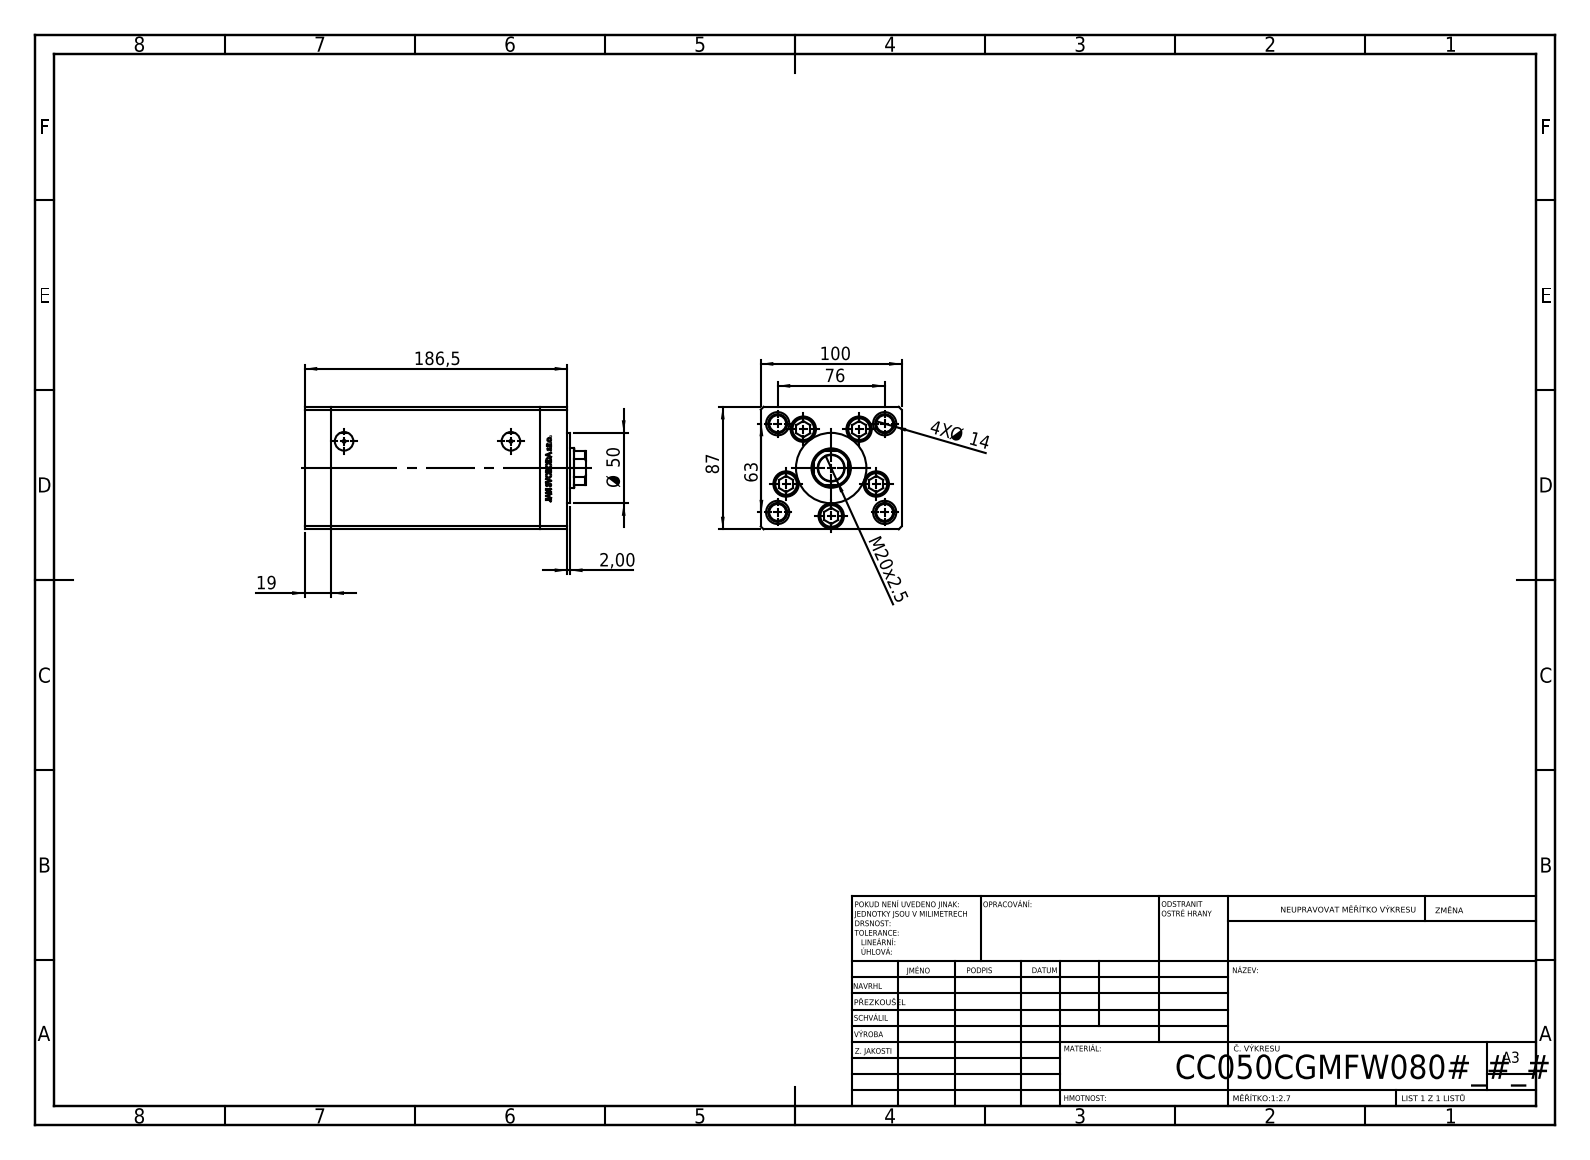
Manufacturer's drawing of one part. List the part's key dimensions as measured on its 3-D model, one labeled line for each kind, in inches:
Part name (STEP PRODUCT): V220C_VC_C; V220C BACK_C; V220C_C MIDDLE; V220C FRONT (+1 more)
STEP written by: SolidWorks 2019 (CONFIG_CONTROL_DESIGN)
Units: inches
Bodies: 13 solids, 1172 faces (542 planar, 168 cylindrical, 462 other)
Overall size (bounding box): 7.854 × 3.937 × 3.425
Volume: 81.28 in³ · Surface area: 356 in²
Round holes (diameter × count): ⌀0.531 ×9, ⌀0.709 ×5, ⌀0.472 ×4, ⌀0.65 ×4, ⌀0.079 ×2, ⌀0.518 ×2, ⌀0.669 ×1, ⌀0.728 ×1, ⌀1.102 ×1
Round bosses / shafts (diameter × count): ⌀0.315 ×5, ⌀0.669 ×4, ⌀1.969 ×1
Partial cylindrical surfaces — rounded edges, fillets, slot ends (radius × count): R0.037 ×2, R0.531 ×1
Main face-to-face distances: 3.937, 3.425, 0.748, 5.846, 6.594, 1.348, 7.343, 5.994, 5.246, 0.6
Hole centre spacings: 1.339, 1.943, 0.732, 0.828, 1.499, 1.546, 1.607, 1.702
